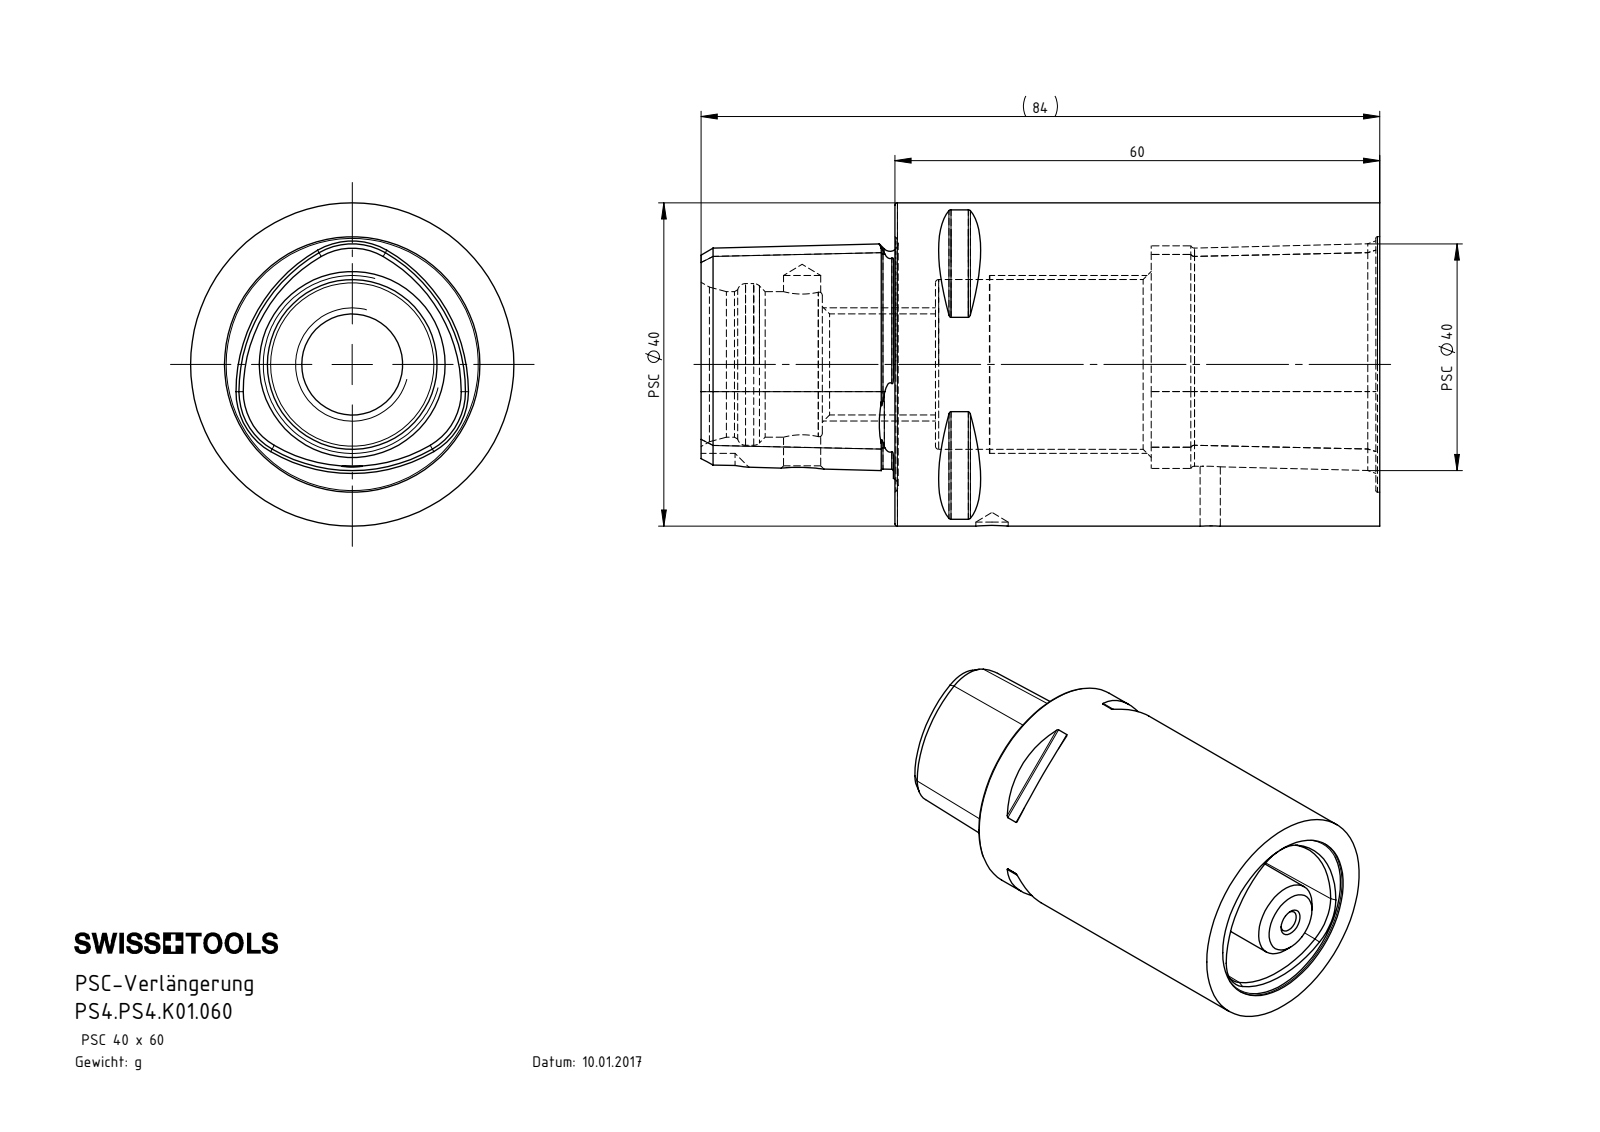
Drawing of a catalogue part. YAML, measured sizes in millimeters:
part_name: "PS4-PS4.K01.060_B; PS4.PS4.K01.060; PS4-ER2.001.017_A; PS4-ER1.K01.047_A_PreviewCfg (+1 more)"
step_written_by: "SolidWorks 2017 (AUTOMOTIVE_DESIGN)"
units: millimeters
bodies: {solids: 4, faces: 247, planar: 53, cylindrical: 56, other: 138}
overall_size: [86, 40, 40]
volume: 69328
surface_area: 24015
round_holes:
  - {diameter: 4, count: 3}
  - {diameter: 2.5, count: 1}
  - {diameter: 4.6, count: 1}
  - {diameter: 12.5, count: 1}
  - {diameter: 14.4, count: 1}
  - {diameter: 18, count: 1}
  - {diameter: 20, count: 1}
  - {diameter: 21, count: 1}
  - {diameter: 31.6, count: 1}
round_bosses_or_shafts:
  - {diameter: 40, count: 1}
  - {diameter: 23.4, count: 1}
  - {diameter: 22, count: 1}
  - {diameter: 19.6, count: 1}
  - {diameter: 18.9, count: 1}
  - {diameter: 14, count: 1}
partial_cylinders:
  - {radius: 0.3, count: 8}
  - {radius: 7.95, count: 3}
  - {radius: 19.58, count: 3}
  - {radius: 3, count: 1}
face_to_face_distances: [60, 5, 55, 24, 34.9, 29.9, 25.1, 31.7, 26.7, 3.2]
hole_center_spacings: [23.5, 27, 50.5]
